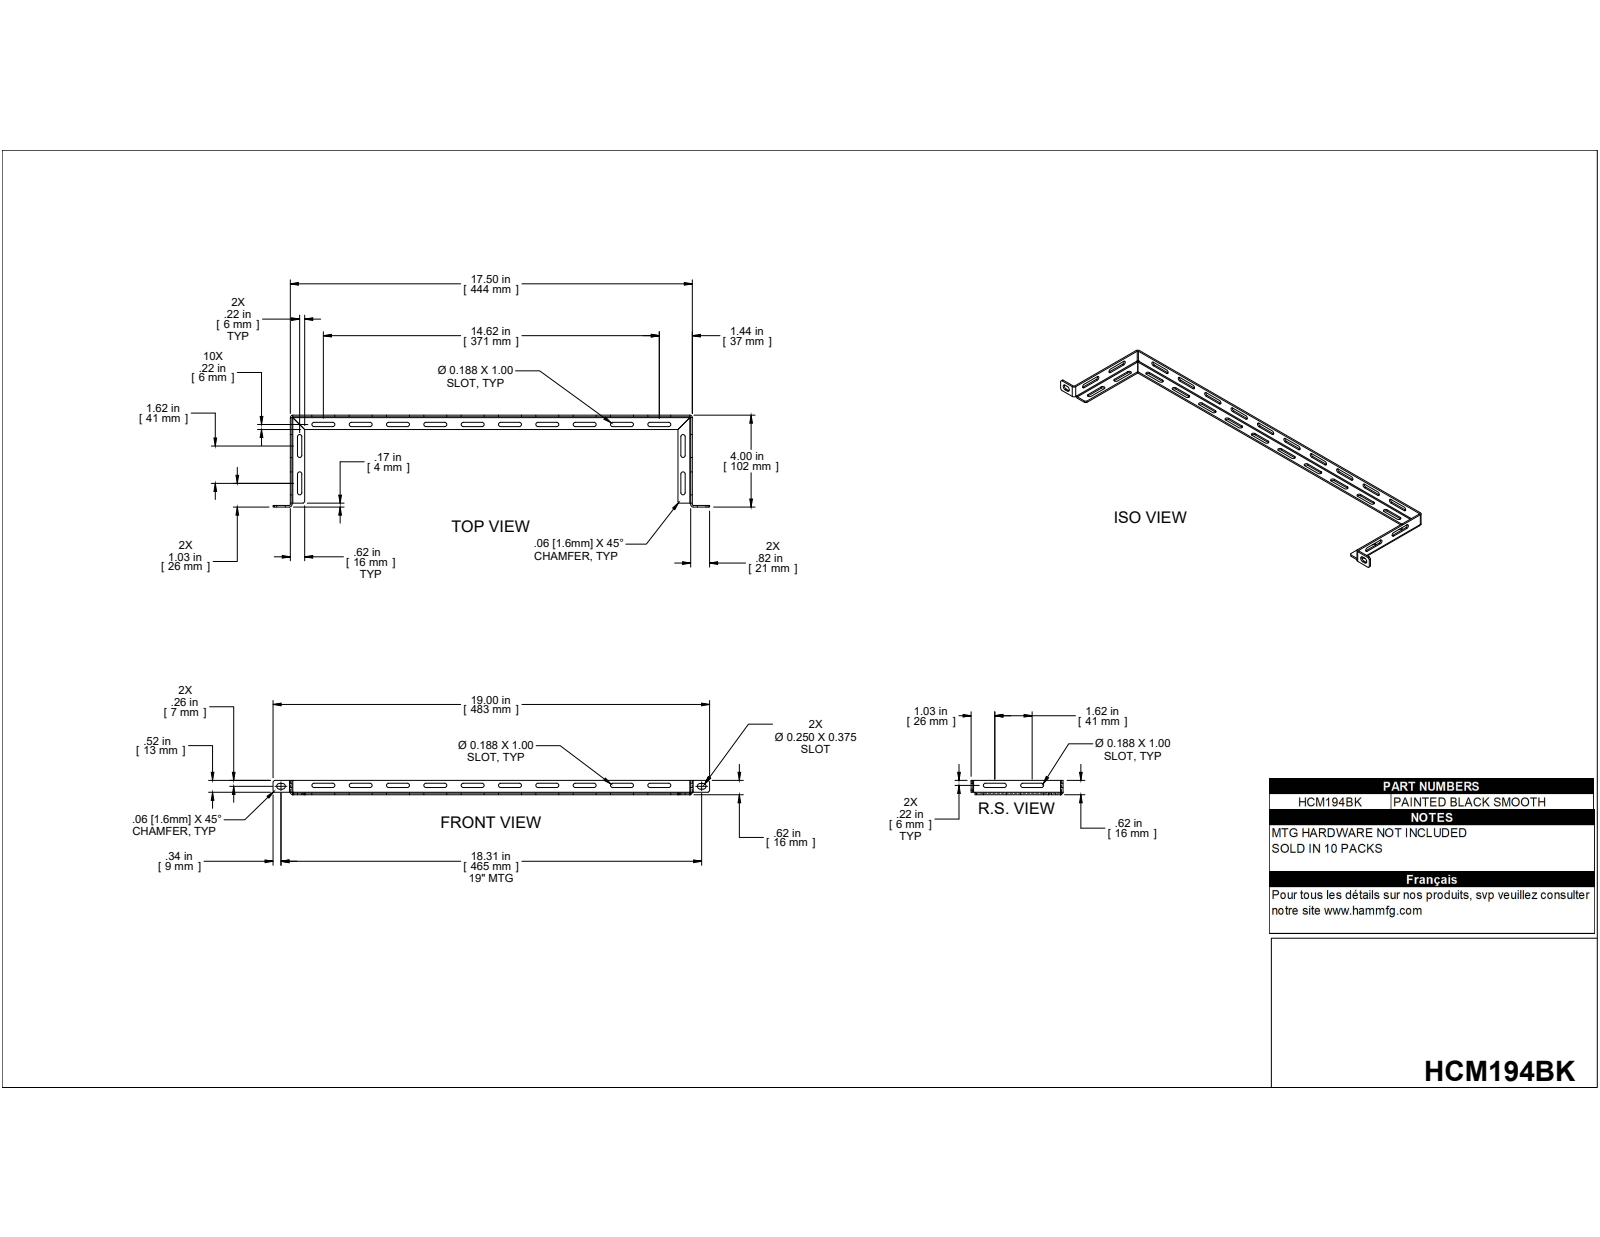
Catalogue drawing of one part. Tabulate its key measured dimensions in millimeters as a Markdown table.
| quantity | value |
| --- | --- |
| part name | COM57141-4 |
| STEP written by | ST-DEVELOPER v16.7 (AUTOMOTIVE_DESIGN) |
| units | millimeters |
| bodies | 1 solid, 180 faces (102 planar, 74 cylindrical, 4 other) |
| overall size | 482.6 × 101.6 × 15.88 |
| volume | 27 907 mm³ |
| surface area | 36 136 mm² |
| partial cylindrical surfaces (radius × count) | 2.38 × 52, 0.91 × 7, 2.74 × 7, 3.17 × 4 |
| main face-to-face distances | 1.83, 442.67, 14.04, 15.87, 7.94, 6.11, 4.76, 10.87, 12.7, 444.5 |
